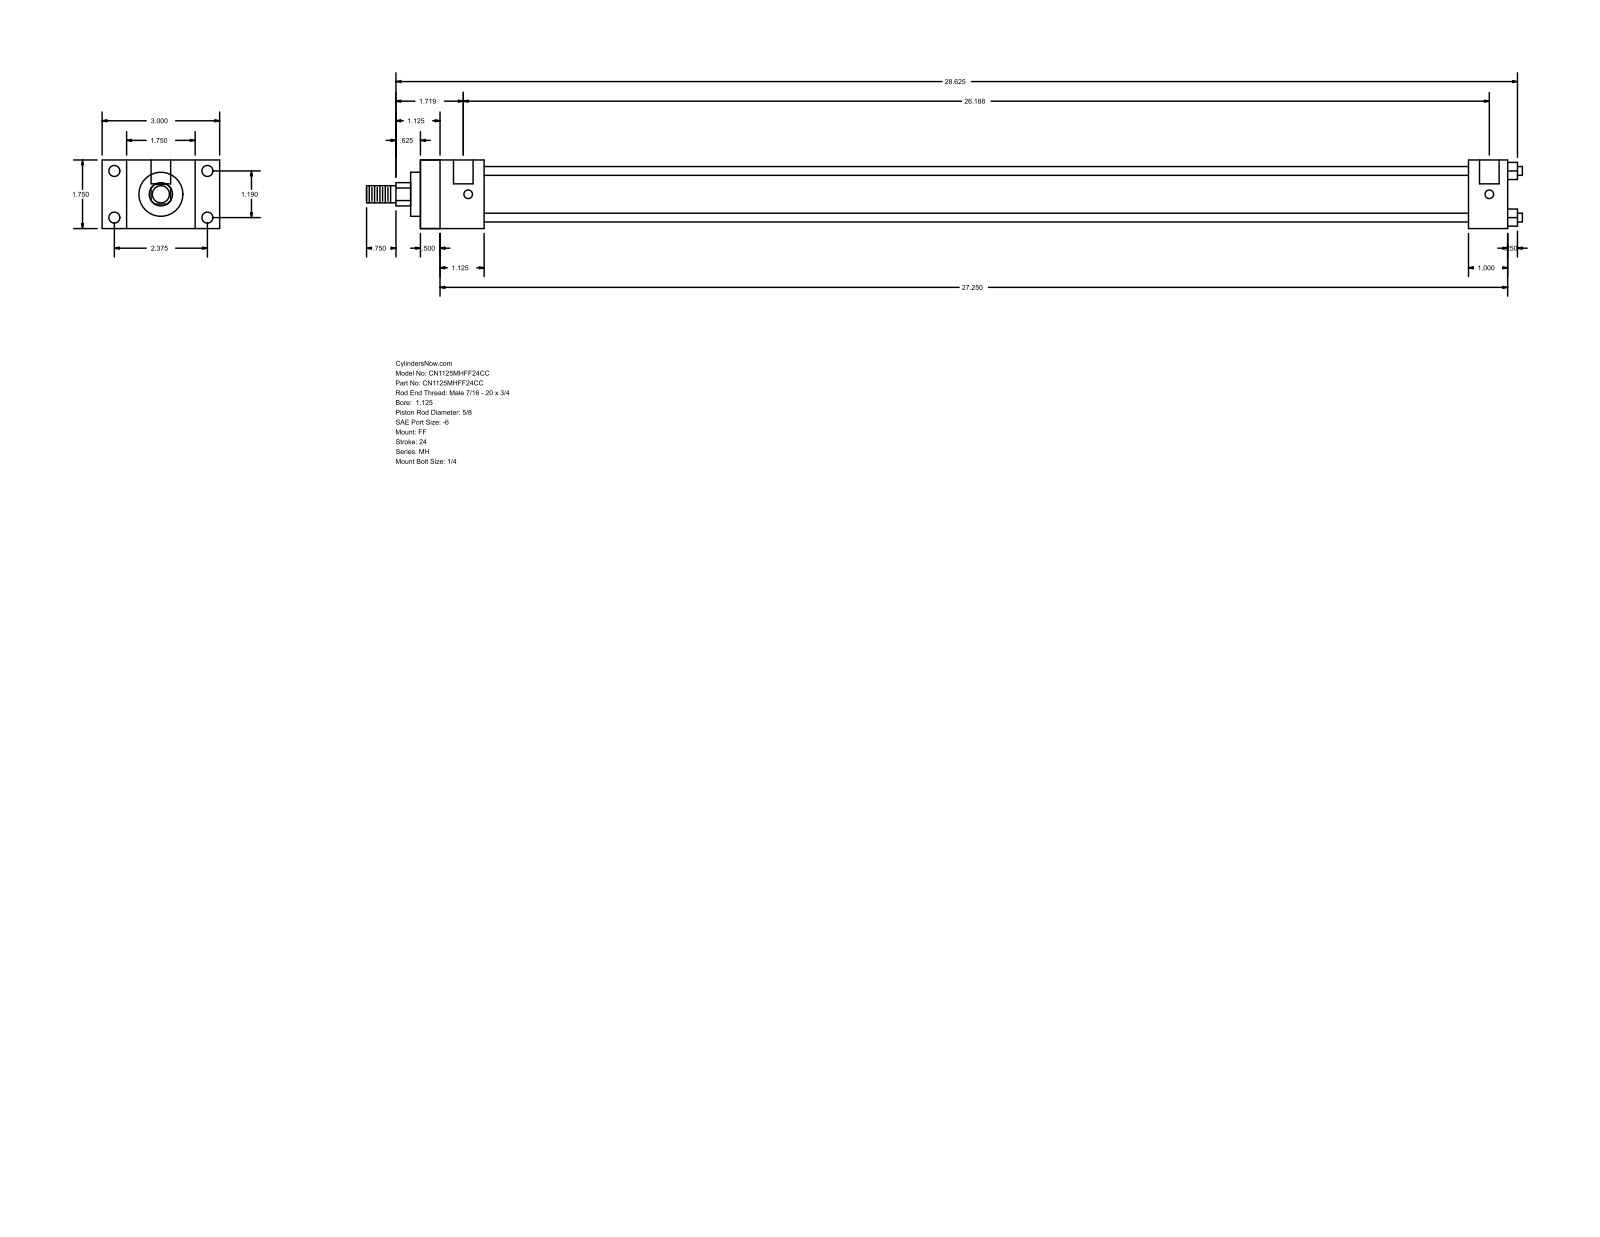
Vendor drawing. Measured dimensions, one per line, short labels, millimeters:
name: MH_FF__0112_0.625
written by: GSSL Pune (CONFIG_CONTROL_DESIGN)
unit: mm
bodies: 0 solids, 92 faces (64 planar, 28 cylindrical, 0 other)
size: 749.3 × 76.2 × 44.45
holes: 4× ⌀5.56, 4× ⌀7.14, 2× ⌀12.7
bosses: 4× ⌀5.71, 1× ⌀34.92, 1× ⌀28.57, 1× ⌀15.88, 1× ⌀11.11
rounds: 1× R7.54
face distances: 44.46, 704.85, 12.69, 692.16, 15.87, 28.58, 60.33, 25.4, 41.27, 679.45
hole spacings: 30.22, 60.32, 67.47, 661.99, 3.17, 665.16
